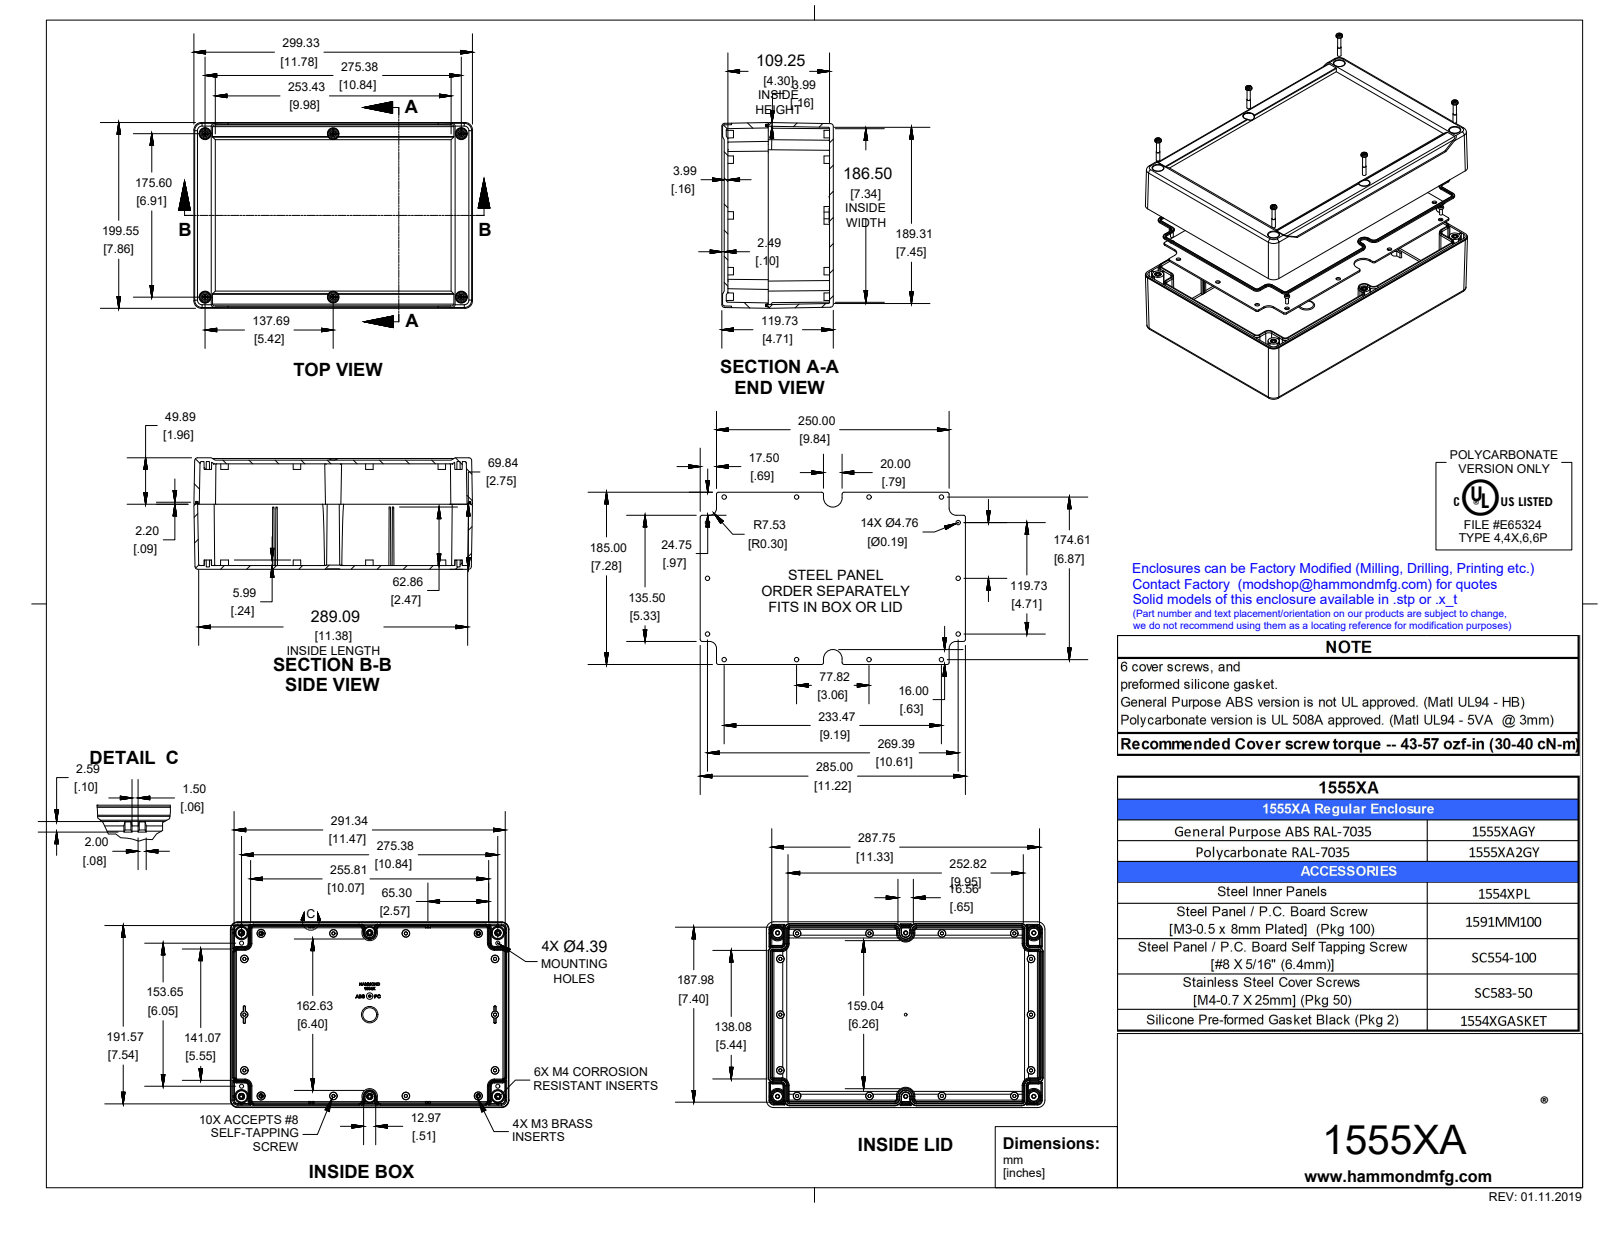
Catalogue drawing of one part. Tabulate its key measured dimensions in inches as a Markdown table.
| quantity | value |
| --- | --- |
| part name | 1555XA2GY |
| STEP written by | SolidWorks 2019 (AUTOMOTIVE_DESIGN) |
| units | inches |
| bodies | 24 solids, 3361 faces (985 planar, 730 cylindrical, 1646 other) |
| overall size | 11.811 × 7.874 × 4.724 |
| volume | 69.12 in³ |
| surface area | 1 040 in² |
| round holes (diameter × count) | 0.187 × 14, 0.128 × 6, 0.142 × 6, 0.097 × 4, 0.276 × 1 |
| round bosses / shafts (diameter × count) | 0.272 × 6, 0.25 × 6, 0.213 × 6, 0.21 × 6, 0.152 × 6, 0.137 × 6, 0.118 × 5, 0.19 × 4 |
| partial cylindrical surfaces (radius × count) | 0.02 × 24, 0.012 × 20, 0.031 × 18, 0.079 × 16, 0.028 × 14, 0.118 × 12, 0.315 × 8, 0.039 × 6 |
| main face-to-face distances | 0.157, 4.469, 0.236, 0.394, 0.064, 0.458, 0.3, 4.311, 4.075, 4.011 |
| hole center spacings | 3.071, 7.543, 0.827, 1.109, 1.294, 1.535, 2.362, 3.467 |
